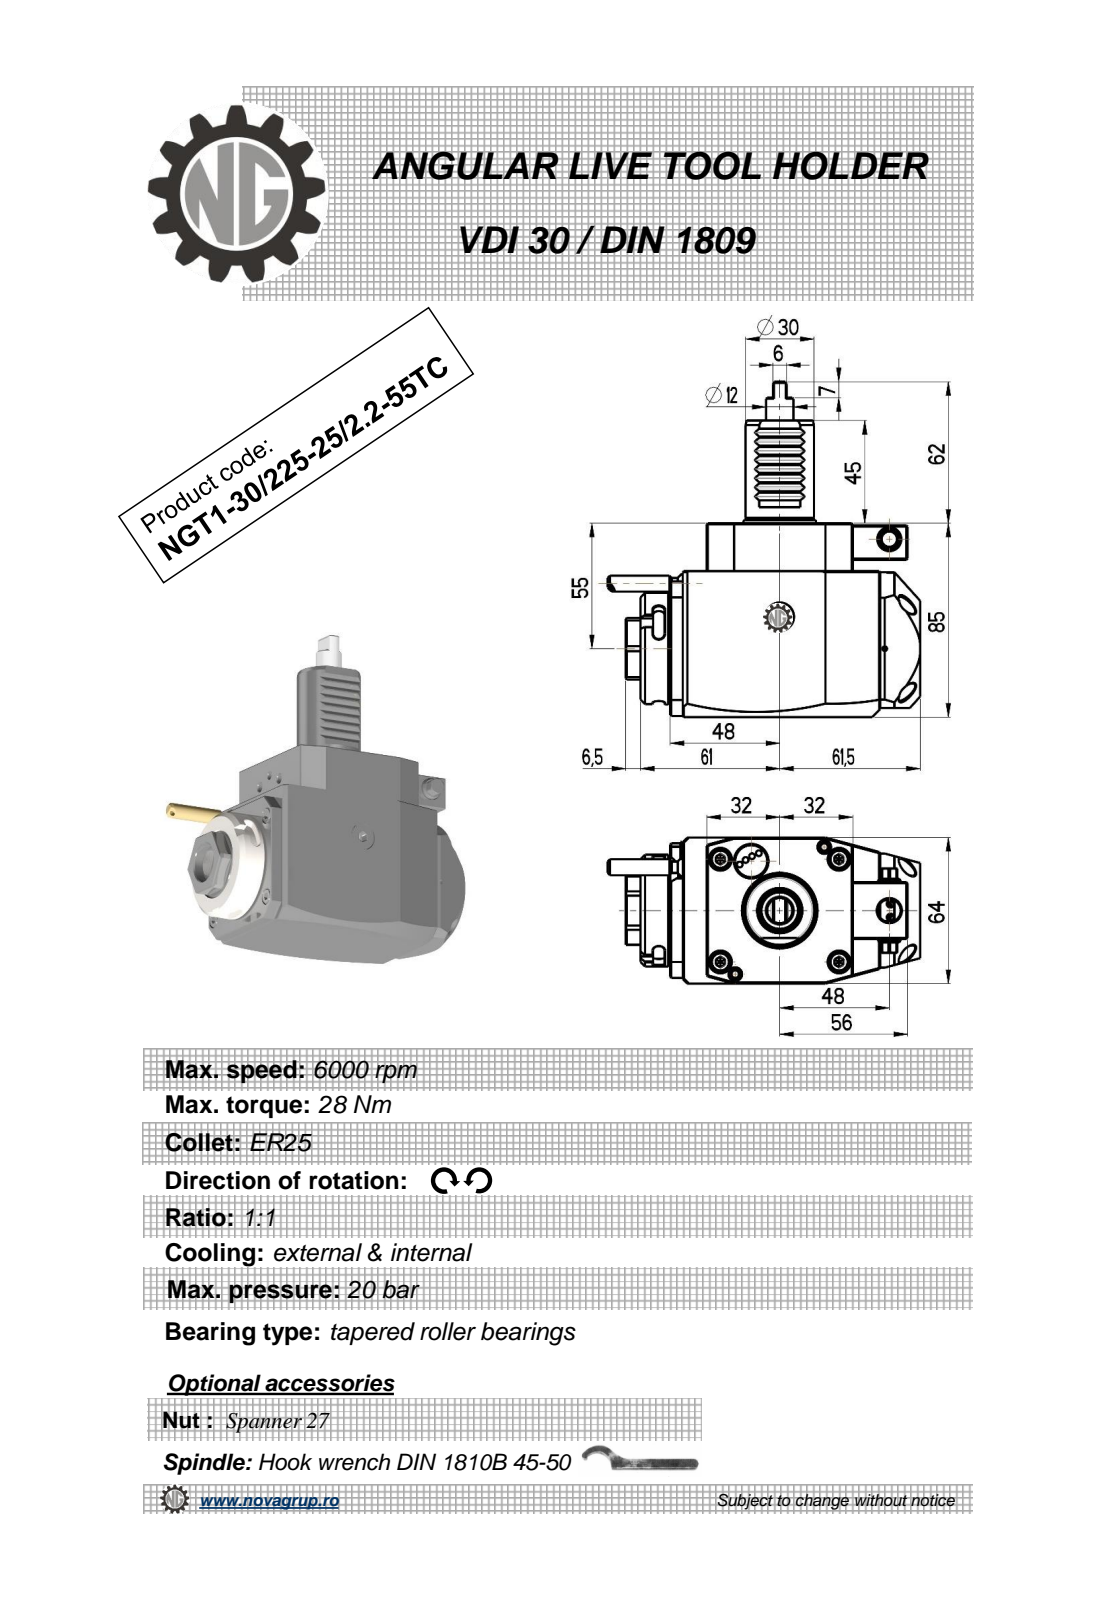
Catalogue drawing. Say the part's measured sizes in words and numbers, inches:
The part is named "NGT1_30_225_25_1_2_55TC". Its 3-D file was written by "PRO/ENGINEER BY PARAMETRIC TECHNOLOGY CORPORATION, 2010280 (CONFIG_CONTROL_DESIGN)". It is 1 solid with 337 faces: 183 planar, 84 cylindrical and 70 other. Overall it measures 5.787 by 5.389 by 2.52 inches. Its volume is 33.62 cubic inches and its surface area 77.32 square inches. Round holes: 1 of diameter 0.098, 1 of diameter 0.118, 1 of diameter 0.374, 1 of diameter 0.394, 1 of diameter 0.709. Round bosses or shafts: 2 of diameter 0.315, 1 of diameter 1.929, 1 of diameter 1.654, 1 of diameter 1.181, 1 of diameter 0.472, 1 of diameter 0.394, 1 of diameter 0.276, 1 of diameter 0.197. Partial cylindrical surfaces (rounded edges, fillets, slot ends): 8 of radius 0.012, 6 of radius 0.098, 2 of radius 0.031, 2 of radius 7.087, 1 of radius 0.152, 1 of radius 0.167, 1 of radius 0.177, 1 of radius 0.591. The main face-to-face distances are 2.52, 3.346, 0.63, 4.311, 0.512, 0.827, 1.142, 3.15, 4.823, 3.681. The hole center spacings are 1.03, 1.348, 1.831.
